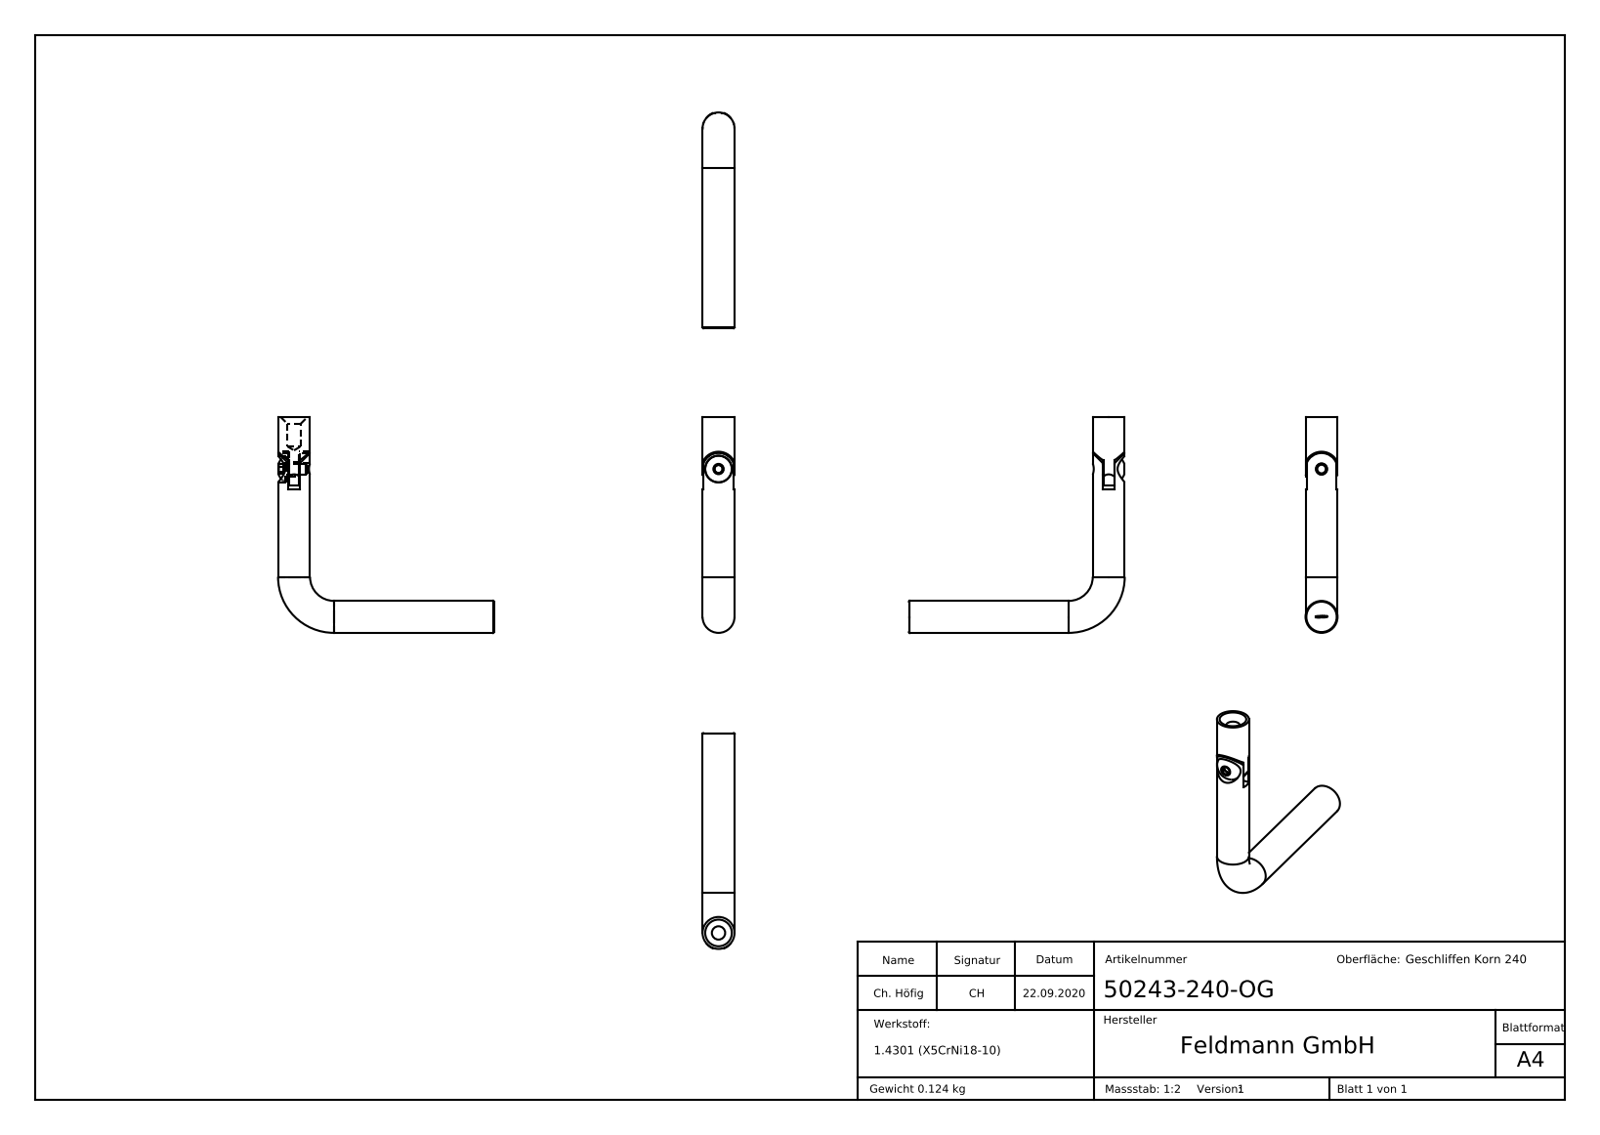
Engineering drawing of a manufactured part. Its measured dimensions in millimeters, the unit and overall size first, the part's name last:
Units: millimetres
Overall size (bounding box): 81 × 81 × 12
Round holes (diameter × count): ⌀4.2 ×1, ⌀5 ×1, ⌀5.5 ×1, ⌀10 ×1
Round bosses / shafts (diameter × count): ⌀12 ×2, ⌀4.02 ×1
Partial cylindrical surfaces — rounded edges, fillets, slot ends (radius × count): R6.5 ×2, R6 ×1
Main face-to-face distances: 4.05, 5.1, 1, 4.1, 78.05, 77.05, 72.95, 1.05, 77, 5.05
Volume: 15 640 mm³ · Surface area: 6 870 mm²
Bodies: 3 solids, 322 faces (159 planar, 25 cylindrical, 138 other)
Part name (STEP PRODUCT): 50243-240-OG Teil1; 50243-240-OG Teil1_50243-240-OG Teil1; 50243-240-OG Teil3; 50243-240-OG Teil3_ISO 7380 M5x8 M5x8 (+3 more)
STEP written by: SolidWorks 2018 (CONFIG_CONTROL_DESIGN)
